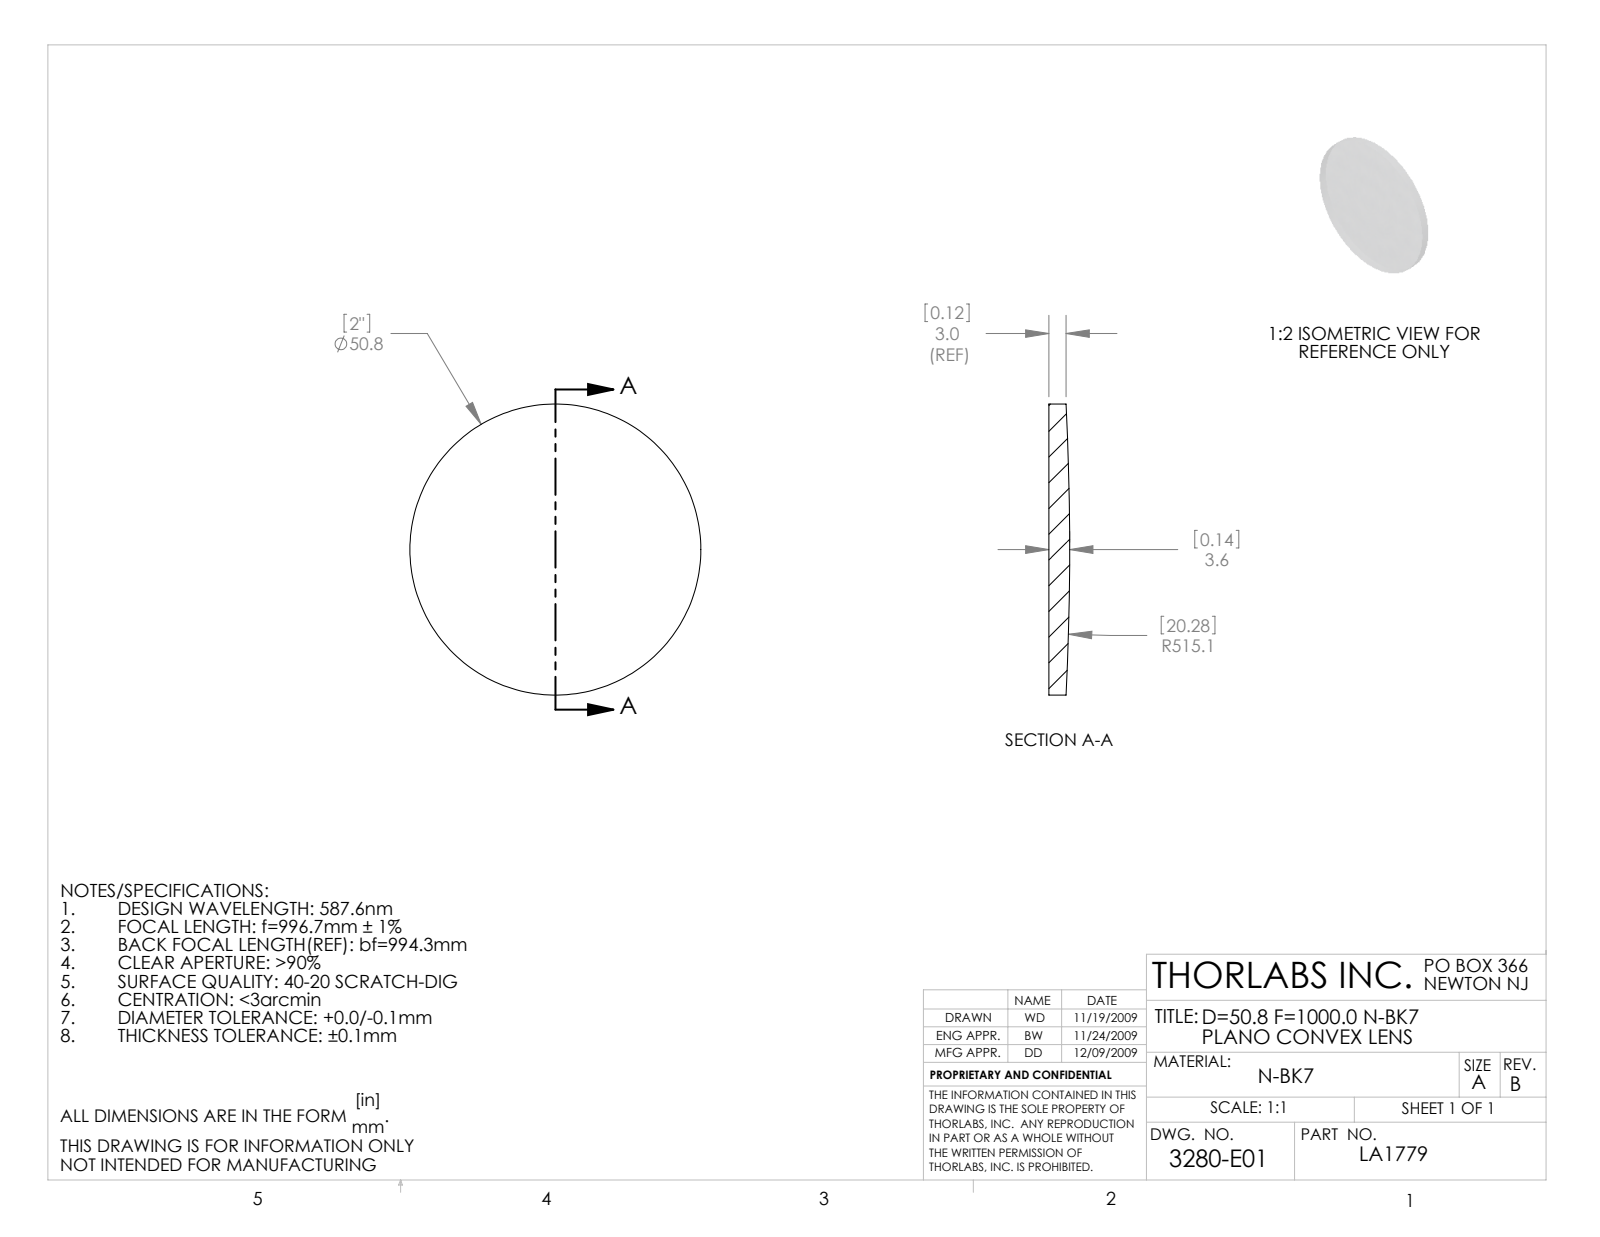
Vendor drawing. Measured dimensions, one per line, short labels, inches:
name: 3280-E0W
written by: SolidWorks 2009 (AUTOMOTIVE_DESIGN)
unit: in
bodies: 1 solid, 5 faces (1 planar, 2 cylindrical, 2 other)
size: 2 × 2 × 0.143
volume: 0.409 in³; area: 7.026 in²
bosses: 1× ⌀2
